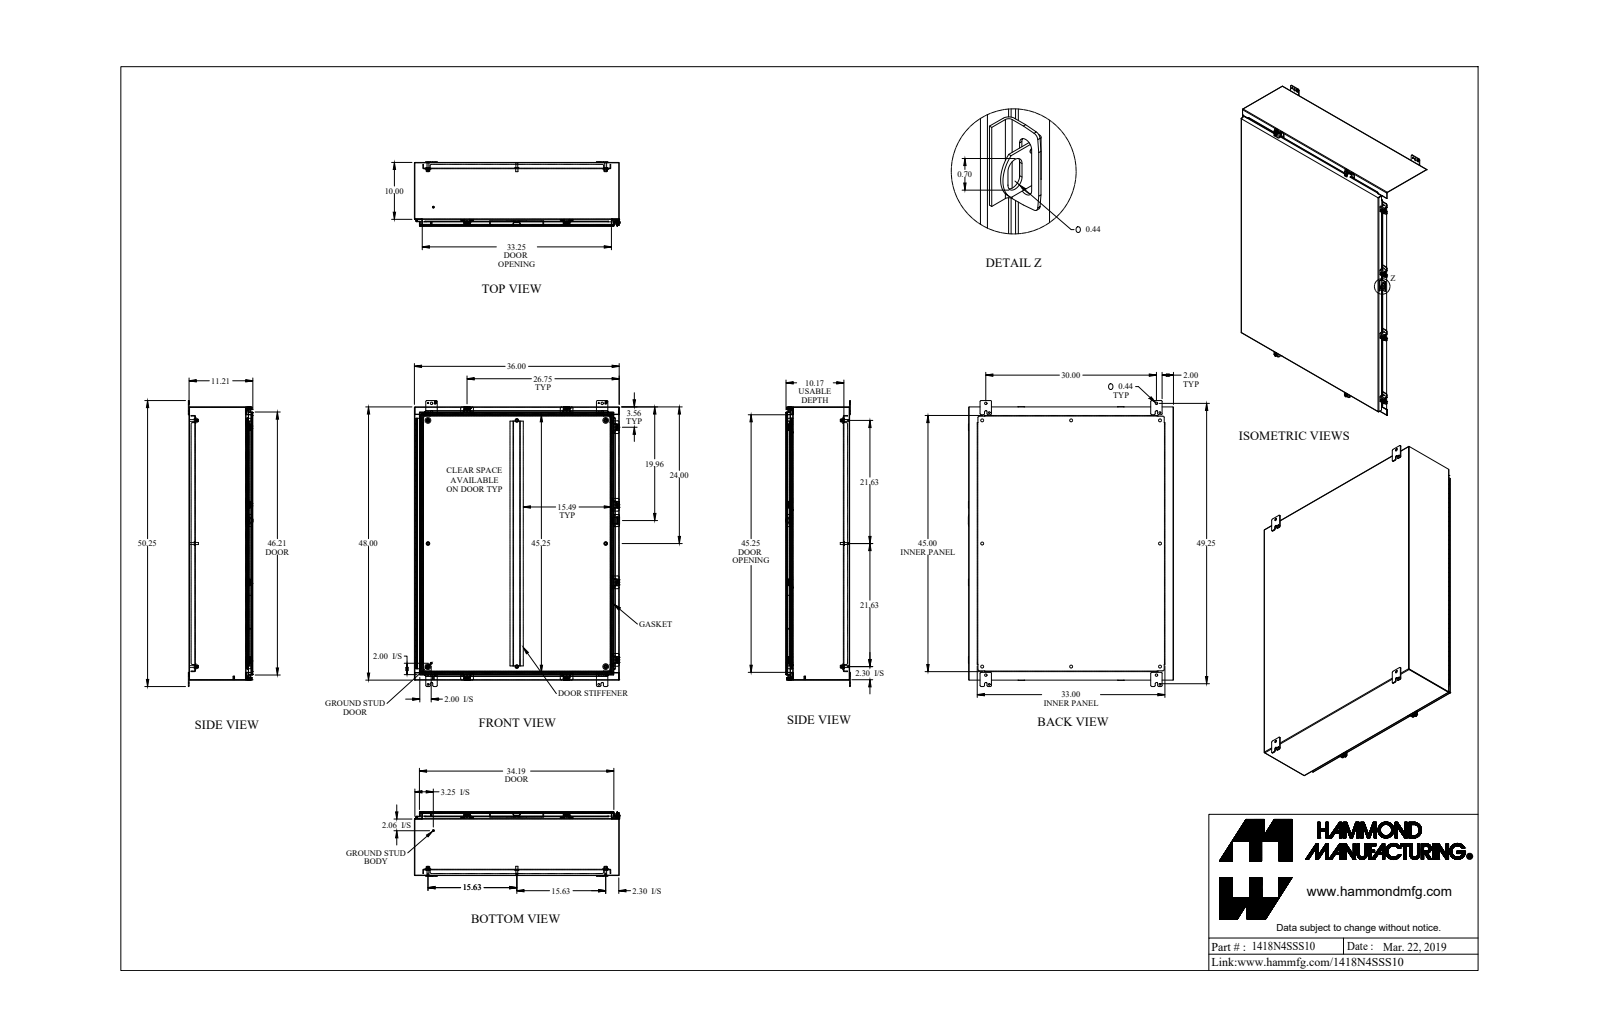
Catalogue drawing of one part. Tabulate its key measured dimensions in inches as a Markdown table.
| quantity | value |
| --- | --- |
| part name | 1418N4SSS10_Default |
| STEP written by | SolidWorks 2019 (CONFIG_CONTROL_DESIGN) |
| units | inches |
| bodies | 66 solids, 2324 faces (1411 planar, 829 cylindrical, 84 other) |
| overall size | 50.25 × 36.063 × 11.375 |
| volume | 585.5 in³ |
| surface area | 15 259 in² |
| round holes (diameter × count) | 0.213 × 8, 0.265 × 8, 0.375 × 8, 0.5 × 8, 0.307 × 4, 0.313 × 4, 0.437 × 4, 0.445 × 4, 0.125 × 1, 0.187 × 1 |
| round bosses / shafts (diameter × count) | 0.65 × 8, 0.5 × 8, 0.39 × 8, 0.375 × 8, 0.332 × 8, 0.244 × 8, 1 × 4, 0.313 × 2 |
| partial cylindrical surfaces (radius × count) | 0.25 × 44, 0.048 × 39, 0.143 × 39, 0.188 × 30, 0.036 × 22, 0.108 × 22, 0.141 × 16, 0.125 × 12 |
| main face-to-face distances | 0.072, 11.066, 11.138, 0.072, 0.095, 11.138, 11.21, 0.937, 1.009, 10.106 |
| hole center spacings | 38.003, 51.507, 7.196, 15.625, 21.625, 24.468, 45.893, 45.986 |
